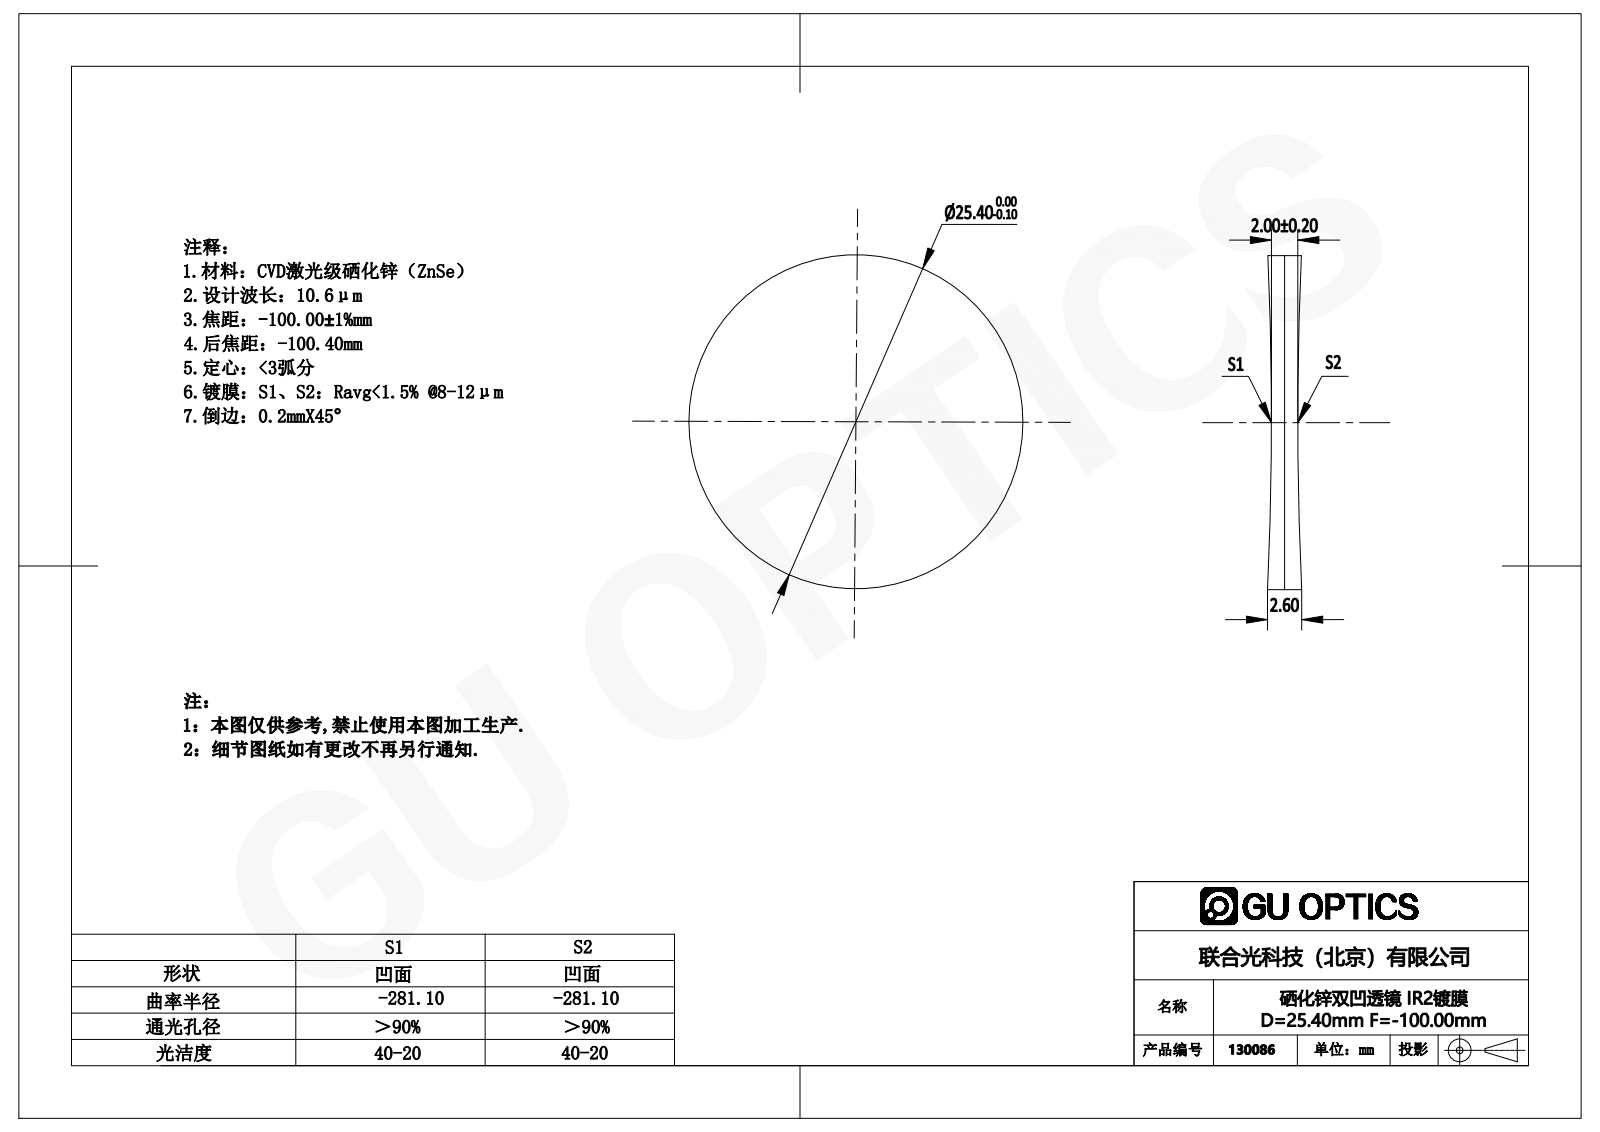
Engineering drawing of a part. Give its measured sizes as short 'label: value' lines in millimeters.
name: 130081
written by: SolidWorks 2016 (AUTOMOTIVE_DESIGN)
unit: mm
bodies: 1 solid, 6 faces (0 planar, 2 cylindrical, 4 other)
size: 25.4 × 25.4 × 2.55
volume: 1 150 mm³; area: 1 217 mm²
bosses: 1× ⌀25.4
